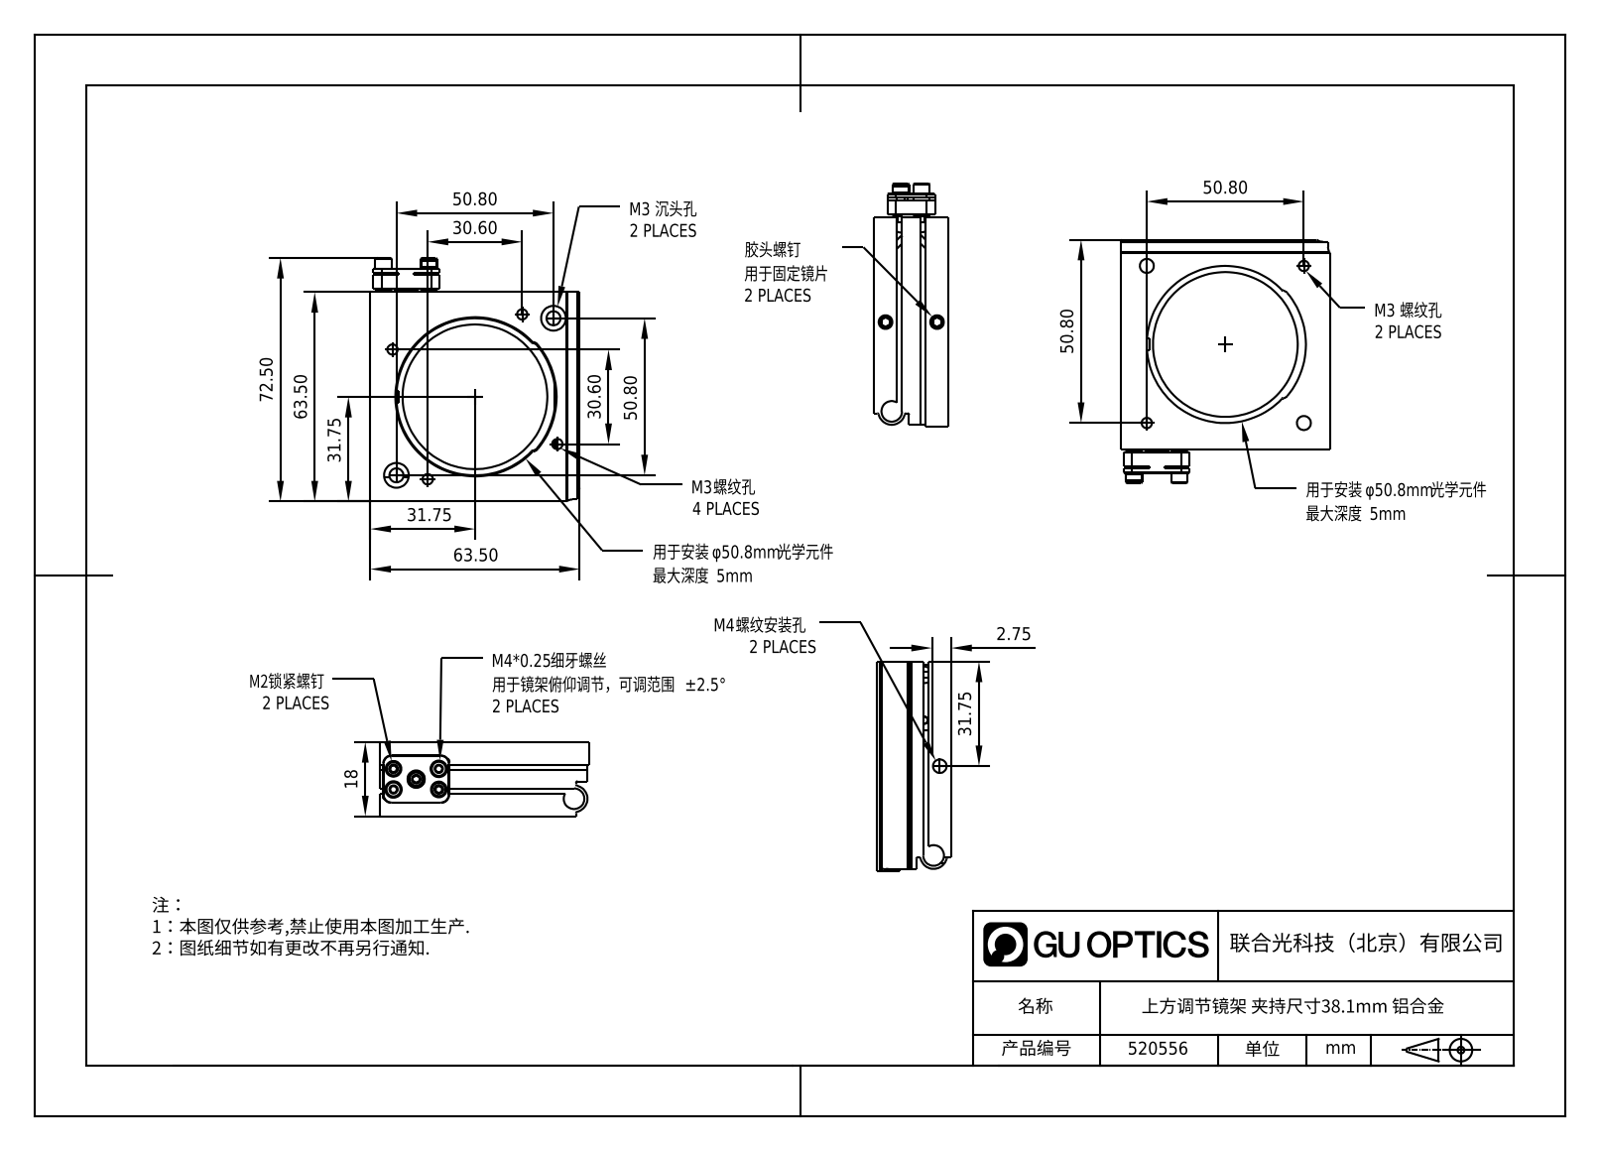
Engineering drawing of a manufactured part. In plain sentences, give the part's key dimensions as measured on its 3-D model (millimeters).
The part is named "耳1.5 440C粣創詩埴翐种_33.2.25-DZ-耳1.5*5; 耳1.5 440C粣創詩埴翐种_33.2.27-DZ-耳1.5*7; 30.1.圆柱头内六角不锈钢螺丝_30.1.18-M2*6; 30.1.圆柱头内六角不锈钢螺丝_30.1.16-M2*4 (+3 more)". Its 3-D file was written by "SolidWorks 2021 (CONFIG_CONTROL_DESIGN)". It is 16 solids with 445 faces: 150 planar, 170 cylindrical and 125 other. Overall it measures 71.91 by 63.5 by 18 millimeters. Its volume is 28 427 cubic millimeters and its surface area 22 937 square millimeters. Round holes: 6 of diameter 2.5, 5 of diameter 3.3, 3 of diameter 1.5, 3 of diameter 1.6, 2 of diameter 2.1, 2 of diameter 3.4, 2 of diameter 5, 2 of diameter 6, 1 of diameter 2.2, 1 of diameter 4, 1 of diameter 47.8. Round bosses or shafts: 5 of diameter 1.5, 3 of diameter 4, 3 of diameter 3.8, 3 of diameter 2, 1 of diameter 3. Partial cylindrical surfaces (rounded edges, fillets, slot ends): 6 of radius 0.35, 6 of radius 2, 4 of radius 1.5, 2 of radius 0.75, 2 of radius 1, 2 of radius 2.25, 2 of radius 2.5, 2 of radius 3.25. The main face-to-face distances are 5.75, 1.25, 6.75, 11.25, 5.5, 12.5, 4.5, 7, 18, 0.5. The hole center spacings are 6.04, 10.2, 30.73, 35.92, 40.7, 43.46, 50.8, 53.03.
